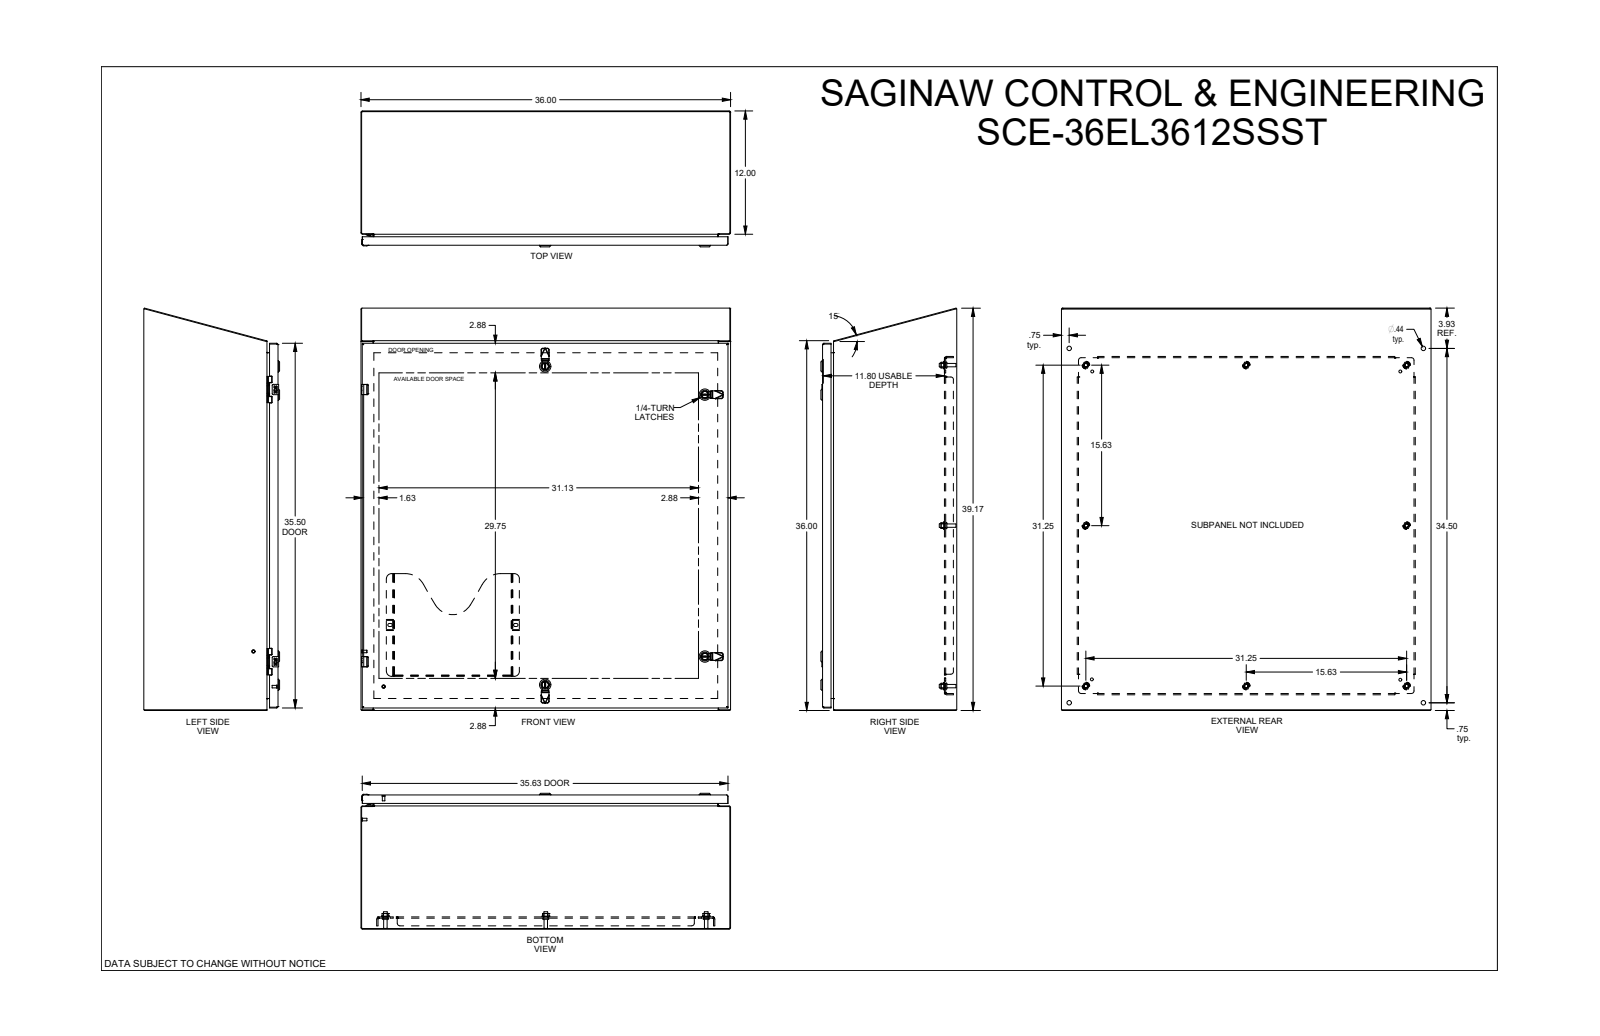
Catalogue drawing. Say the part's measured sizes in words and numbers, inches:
The part is named "SCE-36EL3612SSST". Its 3-D file was written by "SolidWorks 2019 (CONFIG_CONTROL_DESIGN)". It is 0 solids with 3910 faces: 1855 planar, 1049 cylindrical and 1006 other. Overall it measures 39.178 by 36 by 13.23 inches. Round holes: 8 of diameter 0.367, 8 of diameter 0.5, 4 of diameter 0.172, 4 of diameter 0.197, 4 of diameter 0.205, 4 of diameter 0.244, 4 of diameter 0.266, 4 of diameter 0.281, 4 of diameter 0.315, 4 of diameter 0.375, 4 of diameter 0.394, 4 of diameter 0.437. Round bosses or shafts: 8 of diameter 0.366, 8 of diameter 0.332, 6 of diameter 0.17, 4 of diameter 1.102, 4 of diameter 0.866, 4 of diameter 0.802, 4 of diameter 0.78, 4 of diameter 0.63. Partial cylindrical surfaces (rounded edges, fillets, slot ends): 116 of radius 0.012, 52 of radius 0.01, 44 of radius 0.02, 28 of radius 0.015, 23 of radius 0.04, 16 of radius 0.157, 14 of radius 0.07, 12 of radius 0.029. The main face-to-face distances are 0.075, 0.075, 12.998, 12.923, 13.073, 12.998, 1.2, 11.873, 1, 1.125. The hole center spacings are 17.326, 26.5, 0.985, 15.019, 32.334, 0.02, 2.298, 4.493.
